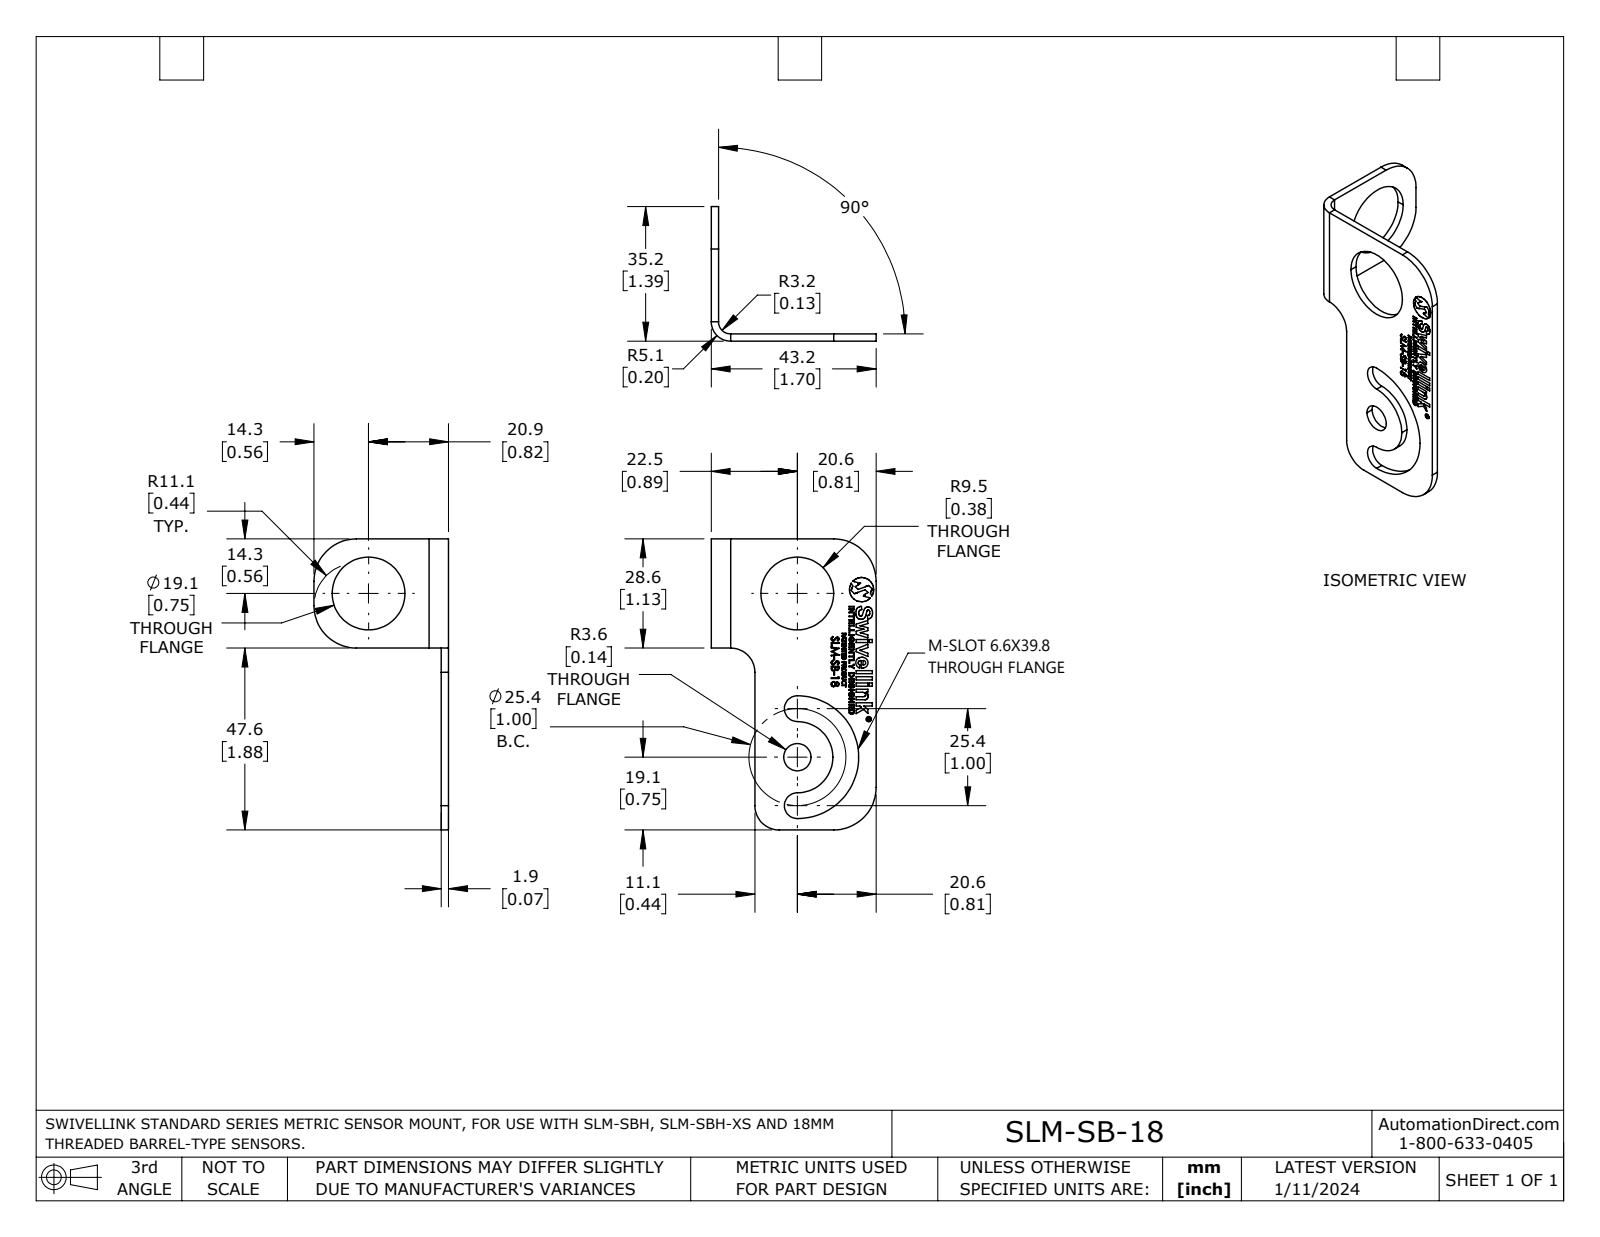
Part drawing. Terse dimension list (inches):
name: SLM-SB-18
written by: SolidWorks 2023 (AUTOMOTIVE_DESIGN)
unit: in
bodies: 1 solid, 109 faces (89 planar, 20 cylindrical, 0 other)
size: 3 × 1.7 × 1.387
volume: 0.304 in³; area: 9.672 in²
holes: 2× ⌀0.75, 1× ⌀0.281
rounds: 4× R0.437, 2× R0.133, 2× R0.25, 1× R0.125, 1× R0.2, 1× R0.367, 1× R0.633
face distances: 0.075, 1.625, 1.7, 1.25, 0.375, 0.45, 1.125, 3, 1.875, 1.312
hole spacings: 1.687
